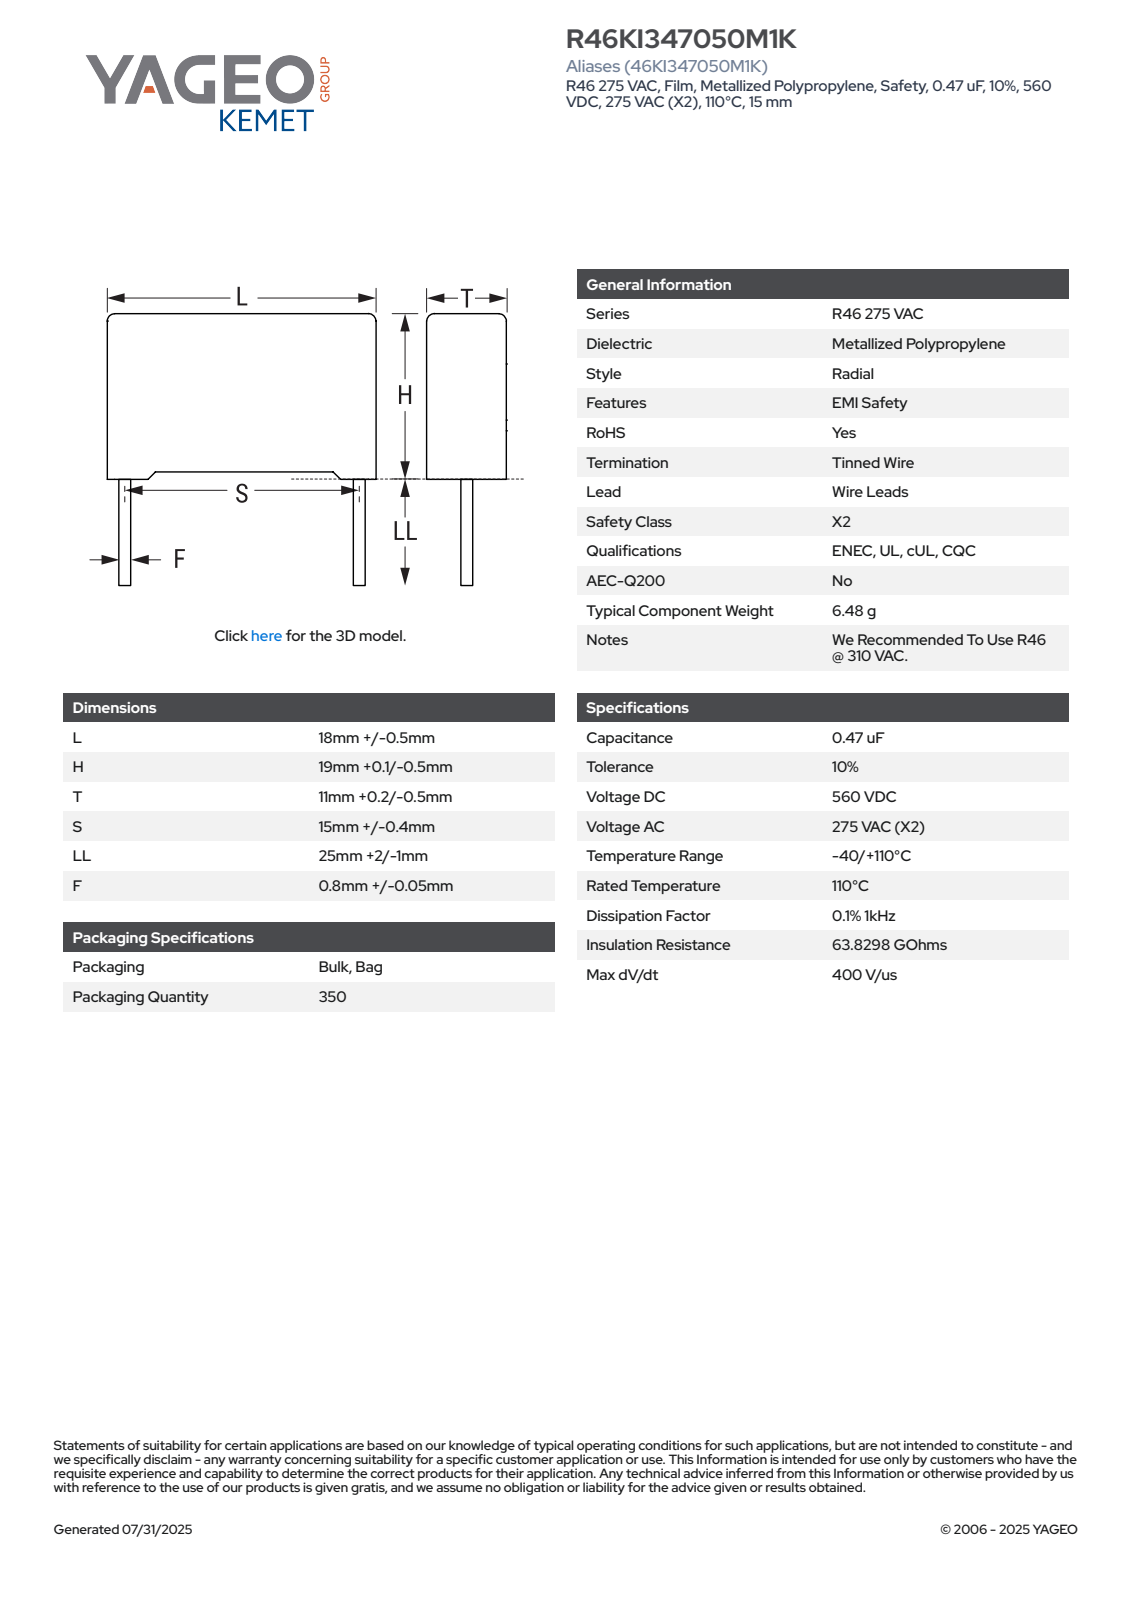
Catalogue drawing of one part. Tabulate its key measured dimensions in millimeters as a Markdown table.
| quantity | value |
| --- | --- |
| part name | CFR_RB2_18X19X11_L18.5H19.1T11.2S15LL27F0.85 |
| STEP written by | SolidWorks 2021 (AUTOMOTIVE_DESIGN) |
| units | millimeters |
| bodies | 4 solids, 85 faces (77 planar, 8 cylindrical, 0 other) |
| overall size | 46.1 × 18.5 × 11.21 |
| volume | 3 848 mm³ |
| surface area | 1 721 mm² |
| round bosses / shafts (diameter × count) | 0.85 × 2 |
| partial cylindrical surfaces (radius × count) | 0.5 × 4 |
| main face-to-face distances | 11.2, 18.5, 18.35, 0.62, 0.75, 19.1, 17.88, 0.66, 18.44, 10.58 |
